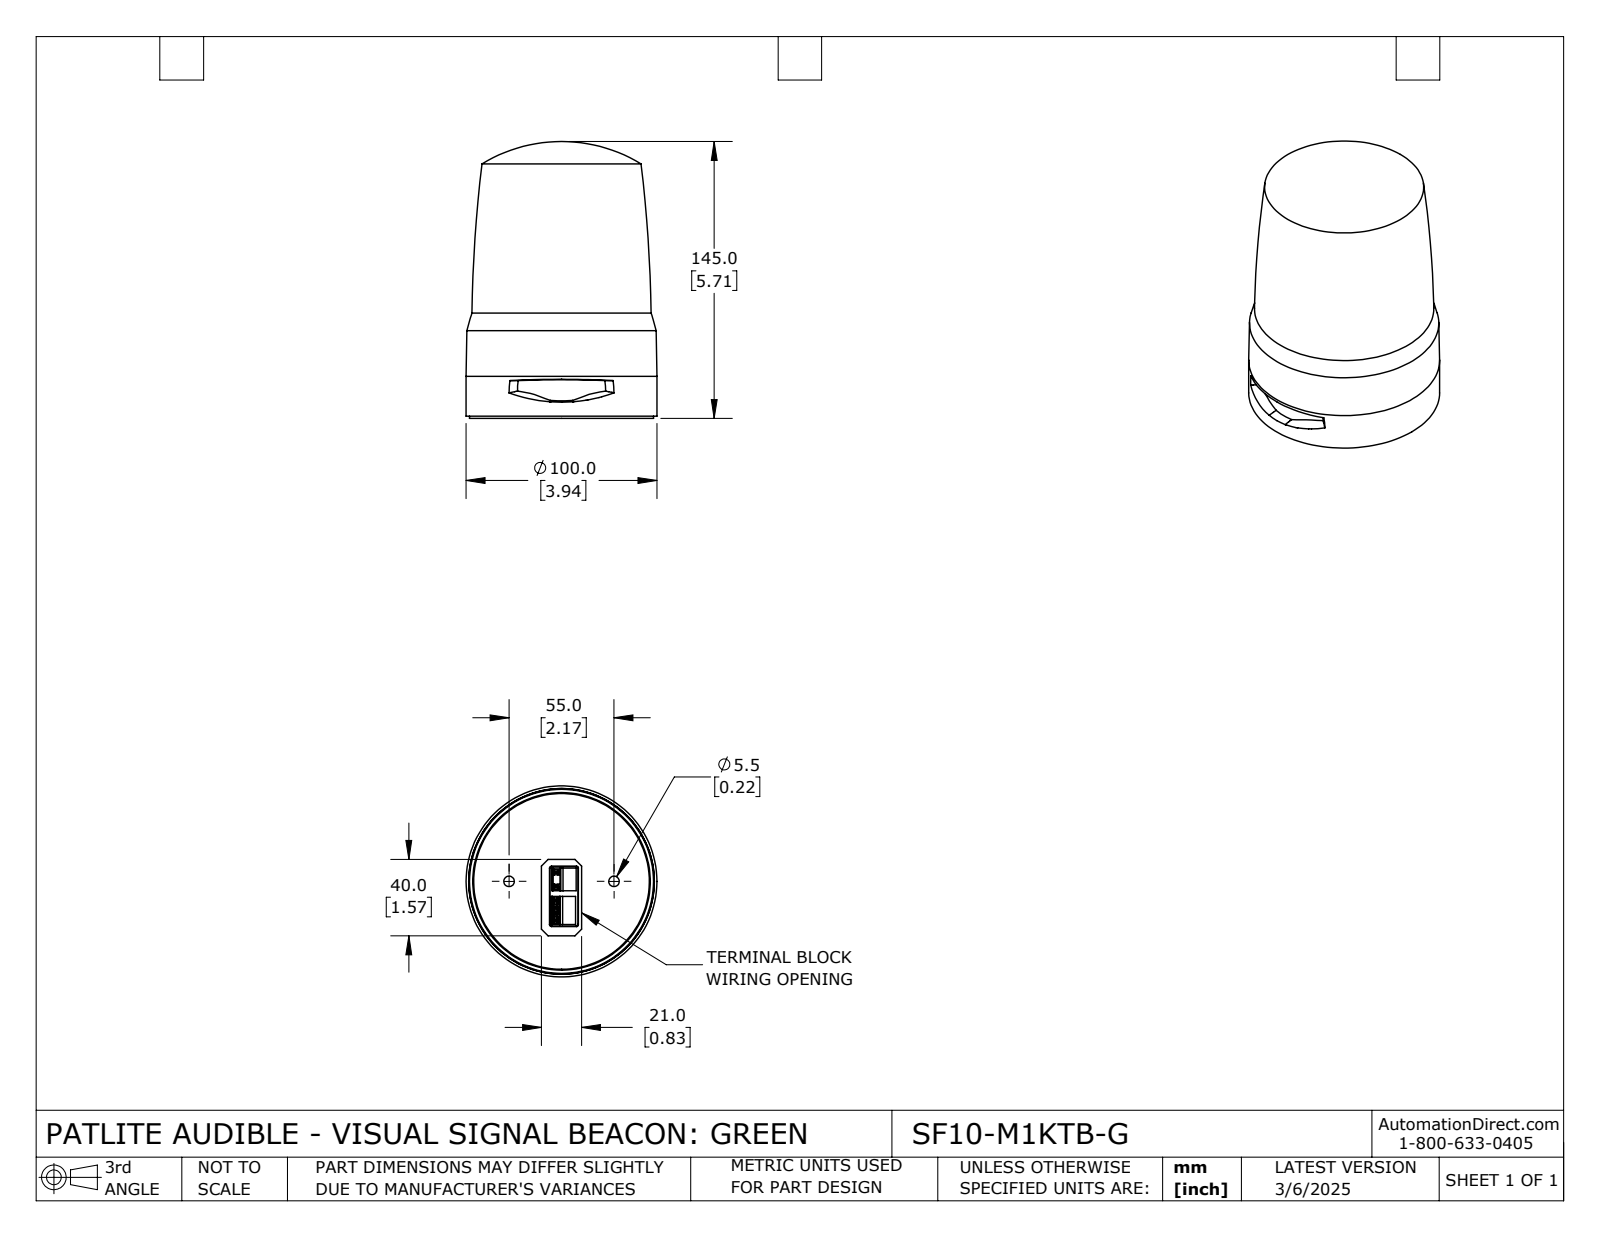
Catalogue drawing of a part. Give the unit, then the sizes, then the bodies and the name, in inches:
Units: inches
Overall size (bounding box): 5.709 × 3.937 × 3.937
Round holes (diameter × count): ⌀0.217 ×2, ⌀0.512 ×2, ⌀3.661 ×1
Round bosses / shafts (diameter × count): ⌀3.937 ×1, ⌀3.795 ×1, ⌀3.72 ×1, ⌀3.669 ×1, ⌀3.622 ×1
Partial cylindrical surfaces — rounded edges, fillets, slot ends (radius × count): R0.039 ×4, R0.012 ×2, R1.762 ×1, R1.772 ×1
Main face-to-face distances: 0.248, 0.717, 0.469, 0.22, 0.496, 0.201, 0.016, 0.185, 0.047, 0.669
Hole centre spacings: 1.083, 2.165
Volume: 53.41 in³ · Surface area: 123.8 in²
Bodies: 2 solids, 275 faces (174 planar, 31 cylindrical, 70 other)
Part name (STEP PRODUCT): SF10-M1KTB-G
STEP written by: SolidWorks 2024 (CONFIG_CONTROL_DESIGN)
